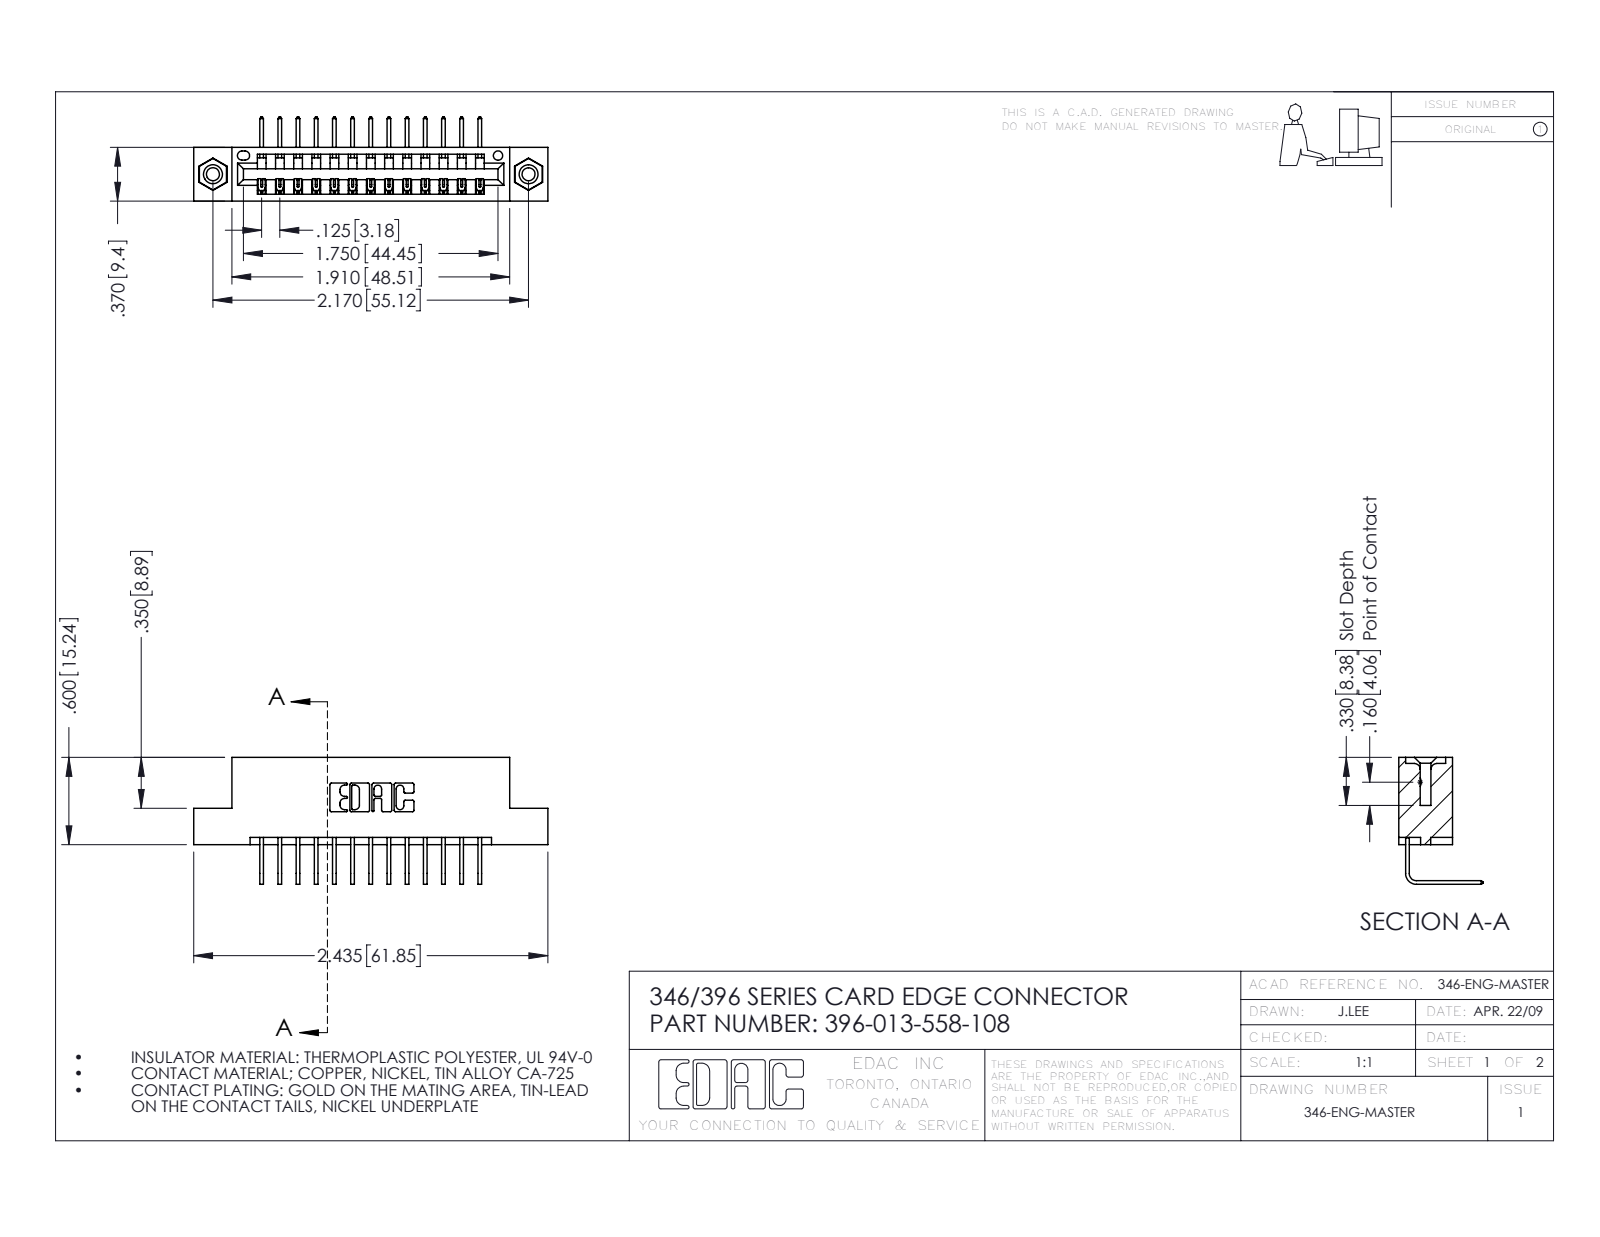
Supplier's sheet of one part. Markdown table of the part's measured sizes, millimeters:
| quantity | value |
| --- | --- |
| part name | 396-013-558-108; 345-250-001_345-250-003-102; 345-292-001_558 Tail - 2; 346 Part_Flush Mounting Lugs - 0.156 Dia-TI |
| STEP written by | SolidWorks 2016 (CONFIG_CONTROL_DESIGN) |
| units | millimeters |
| bodies | 16 solids, 962 faces (654 planar, 292 cylindrical, 16 other) |
| overall size | 61.8 × 22.2 × 14.7 |
| volume | 5 750 mm³ |
| surface area | 7 161 mm² |
| round holes (diameter × count) | 2.3 × 2, 3.2 × 2, 4 × 2, 1.6 × 1 |
| round bosses / shafts (diameter × count) | 3.9 × 2 |
| partial cylindrical surfaces (radius × count) | 0.2 × 26, 0.3 × 22, 0.2 × 6, 0.8 × 6, 0.7 × 3, 0.8 × 2, 1 × 2, 0.4 × 1 |
| main face-to-face distances | 6.4, 8.2, 1.2, 9.4, 7.6, 0.6, 1.8, 3.8, 5.6, 2.5 |
| hole center spacings | 6.2, 49.9, 55.1 |
